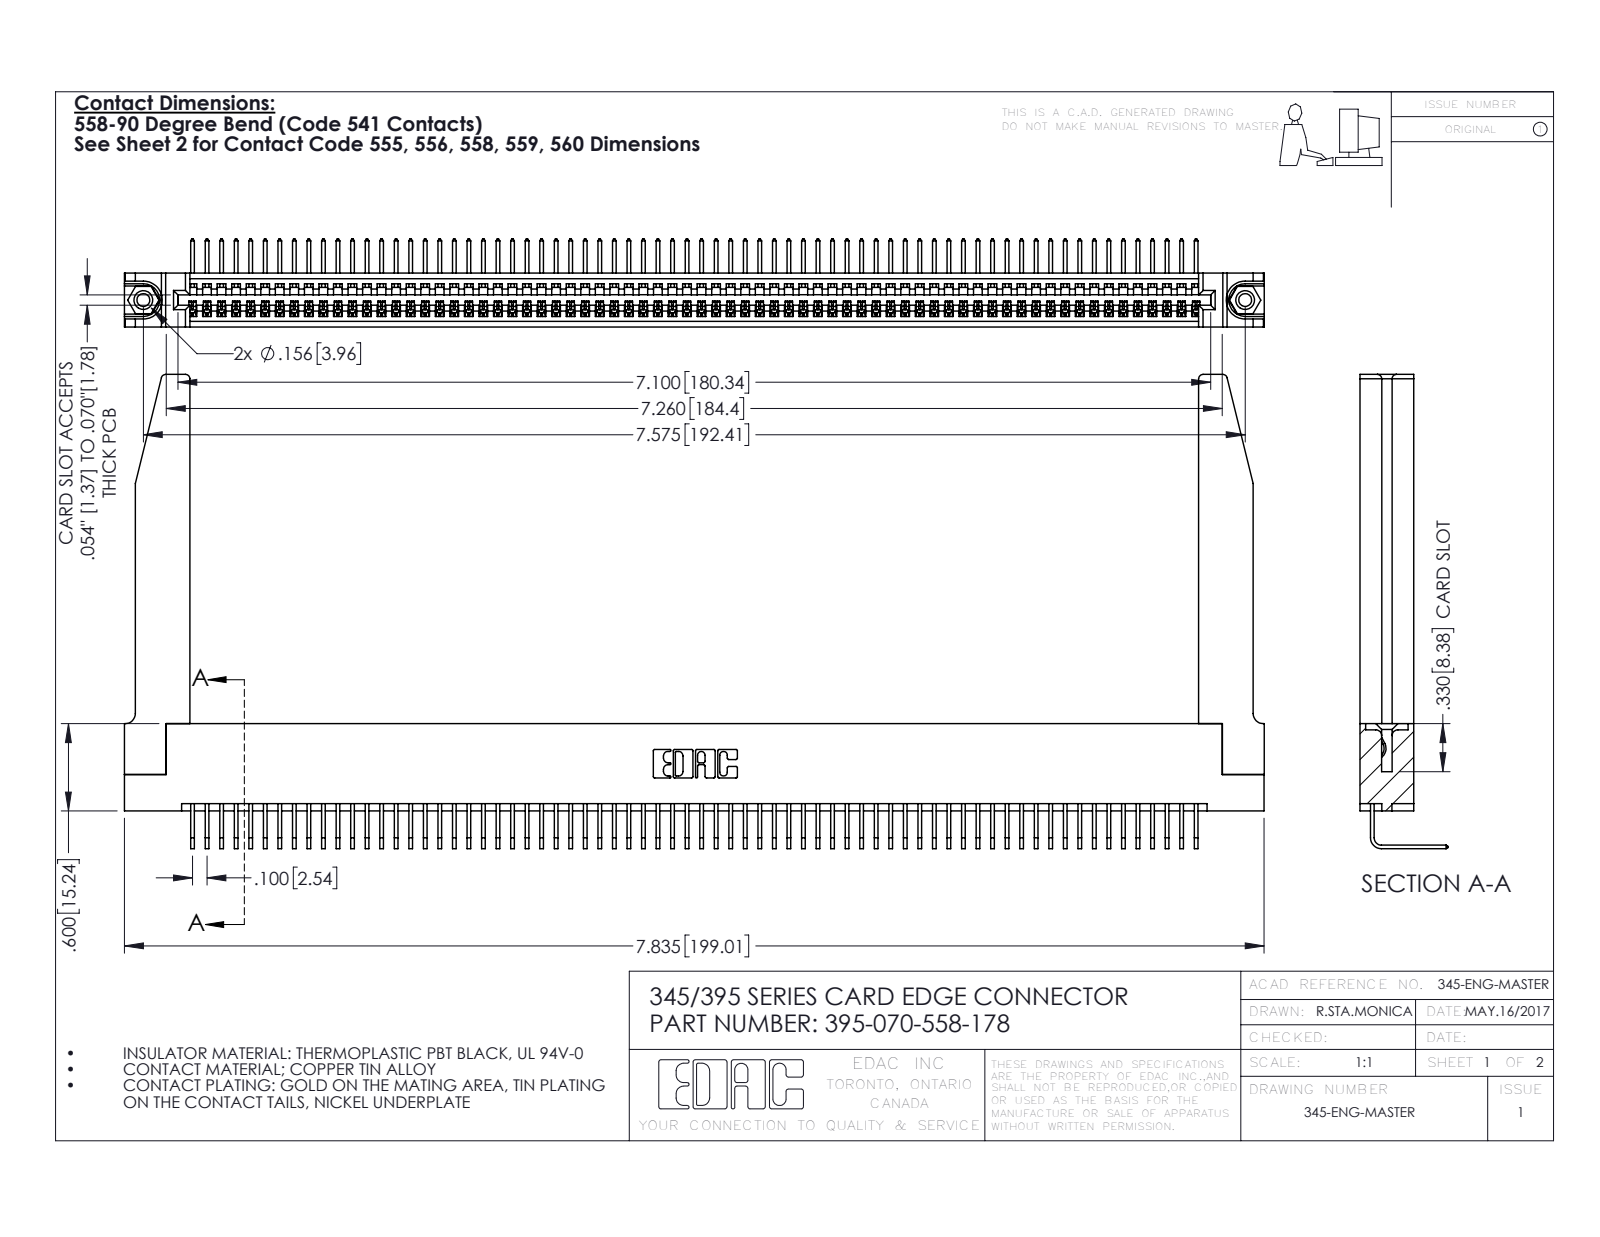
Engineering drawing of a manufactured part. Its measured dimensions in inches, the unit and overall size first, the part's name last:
Units: inches
Overall size (bounding box): 7.836 × 3.259 × 0.605
Round holes (diameter × count): ⌀0.089 ×2, ⌀0.125 ×2, ⌀0.156 ×2, ⌀0.064 ×1
Round bosses / shafts (diameter × count): ⌀0.155 ×2
Partial cylindrical surfaces — rounded edges, fillets, slot ends (radius × count): R0.006 ×140, R0.01 ×22, R0.03 ×8, R0.007 ×6, R0.031 ×6, R0.026 ×3, R0.031 ×2, R0.04 ×2
Main face-to-face distances: 0.072, 0.37, 0.298, 0.2, 0.098, 0.272, 0.025, 0.225, 0.149, 0.148
Hole centre spacings: 0.27, 7.339, 7.575
Volume: 1.656 in³ · Surface area: 53.22 in²
Bodies: 75 solids, 4560 faces (3162 planar, 1346 cylindrical, 52 other)
Part name (STEP PRODUCT): 345 Part_Flush Mounting Lugs - 0.156 Dia-TH; 345-250-001_345-250-001-102; 345-220-078_345-220-078; 395-070-558-178 (+1 more)
STEP written by: SolidWorks 2016 (CONFIG_CONTROL_DESIGN)
